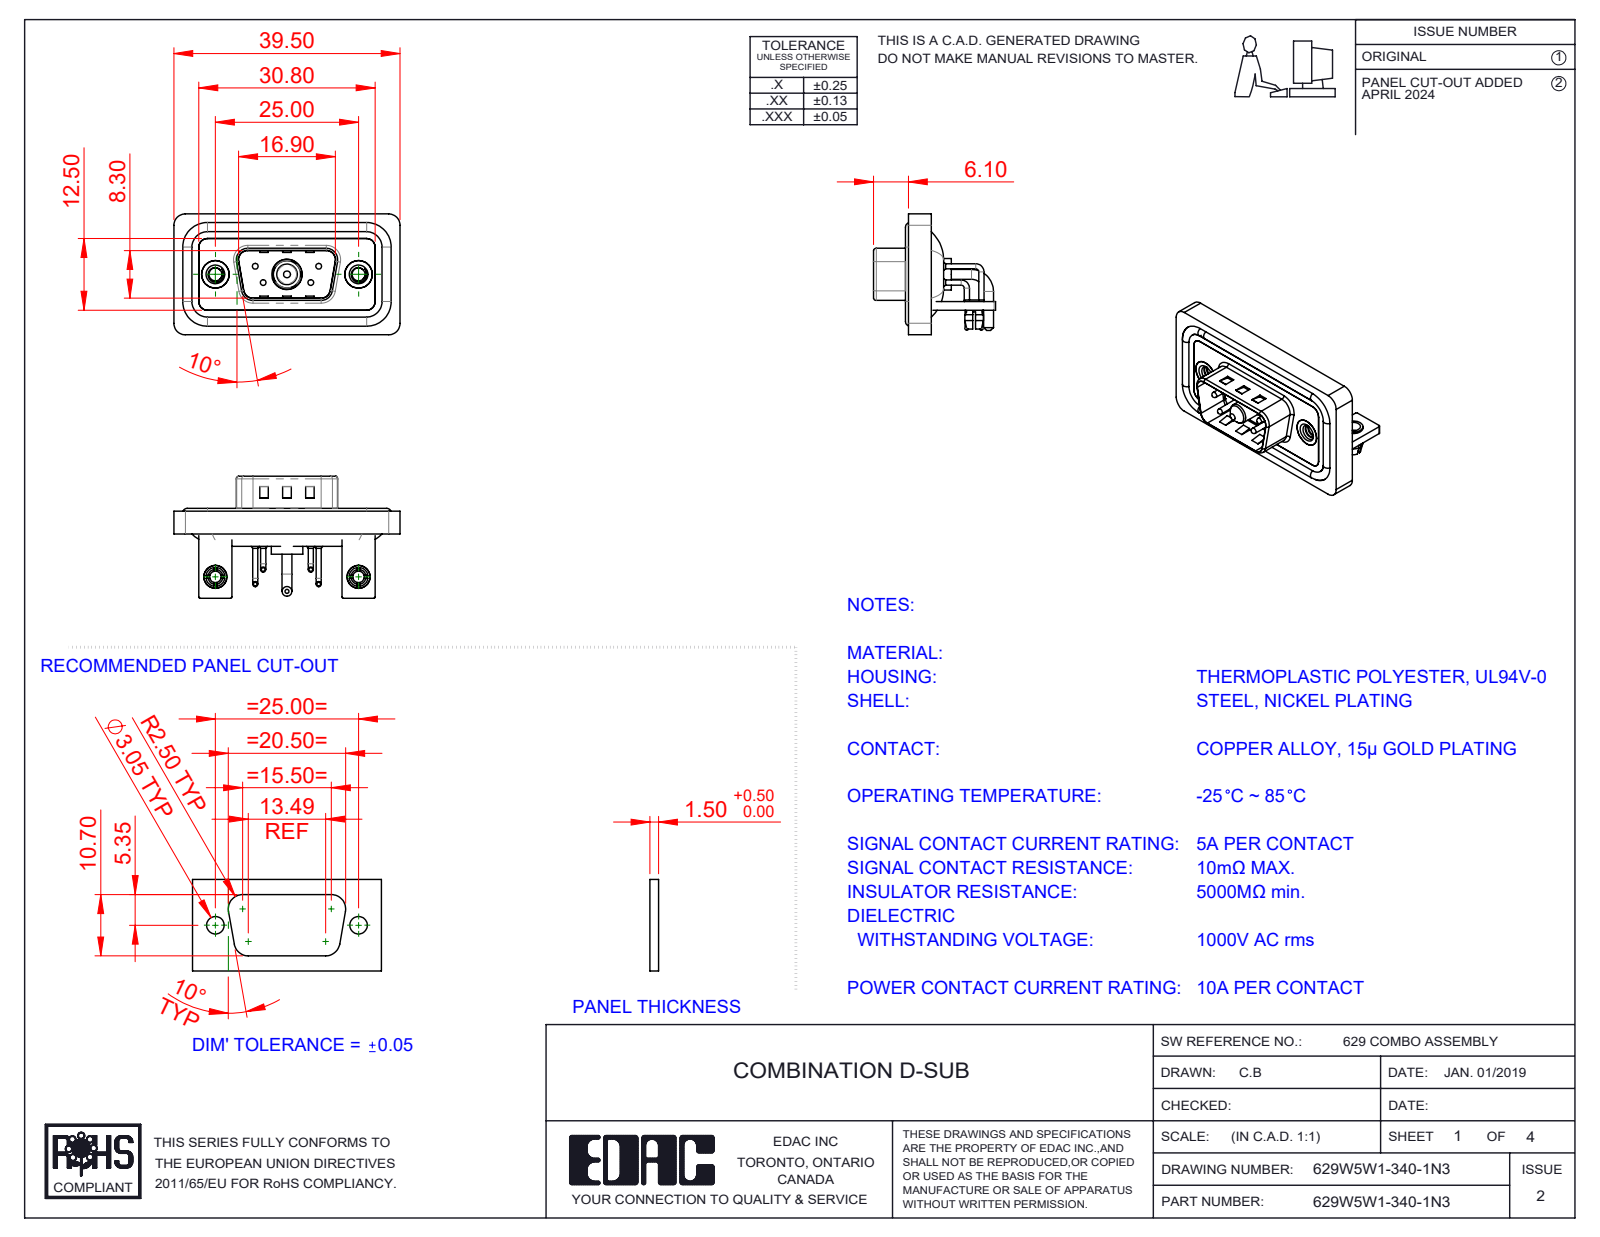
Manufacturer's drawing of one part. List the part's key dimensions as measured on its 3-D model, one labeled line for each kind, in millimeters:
Part name (STEP PRODUCT): 629Combo Contact Row 1; 629Combo Housing_5W1; 629Combo Shell Front_09 Contacts; 629Combo Stabilizer Bracket (+7 more)
STEP written by: SolidWorks 2023 (CONFIG_CONTROL_DESIGN)
Units: millimetres
Bodies: 17 solids, 1026 faces (479 planar, 395 cylindrical, 152 other)
Overall size (bounding box): 39.5 × 21.3 × 21.1
Volume: 4 732 mm³ · Surface area: 7 910 mm²
Round holes (diameter × count): ⌀2 ×6, ⌀0.75 ×4, ⌀1.6 ×4, ⌀2.26 ×2, ⌀2.5 ×2, ⌀3.2 ×2, ⌀4 ×2, ⌀4.8 ×2, ⌀5 ×2, ⌀4.85 ×1, ⌀5.3 ×1
Round bosses / shafts (diameter × count): ⌀0.9 ×8, ⌀1.6 ×4, ⌀1.5 ×4, ⌀1 ×4, ⌀0.65 ×4, ⌀4.9 ×2, ⌀4 ×2, ⌀3.4 ×2
Partial cylindrical surfaces — rounded edges, fillets, slot ends (radius × count): R2 ×19, R1.5 ×18, R0.25 ×16, R0.5 ×9, R1.6 ×8, R0.6 ×4, R0.65 ×4, R0.9 ×4
Main face-to-face distances: 0.4, 1.5, 0.8, 2.9, 1.1, 2.1, 1.2, 1.6, 2.5, 3.7
Hole centre spacings: 3.16, 5.72, 7.1, 12.5, 18.1, 25, 4.39, 4.4
